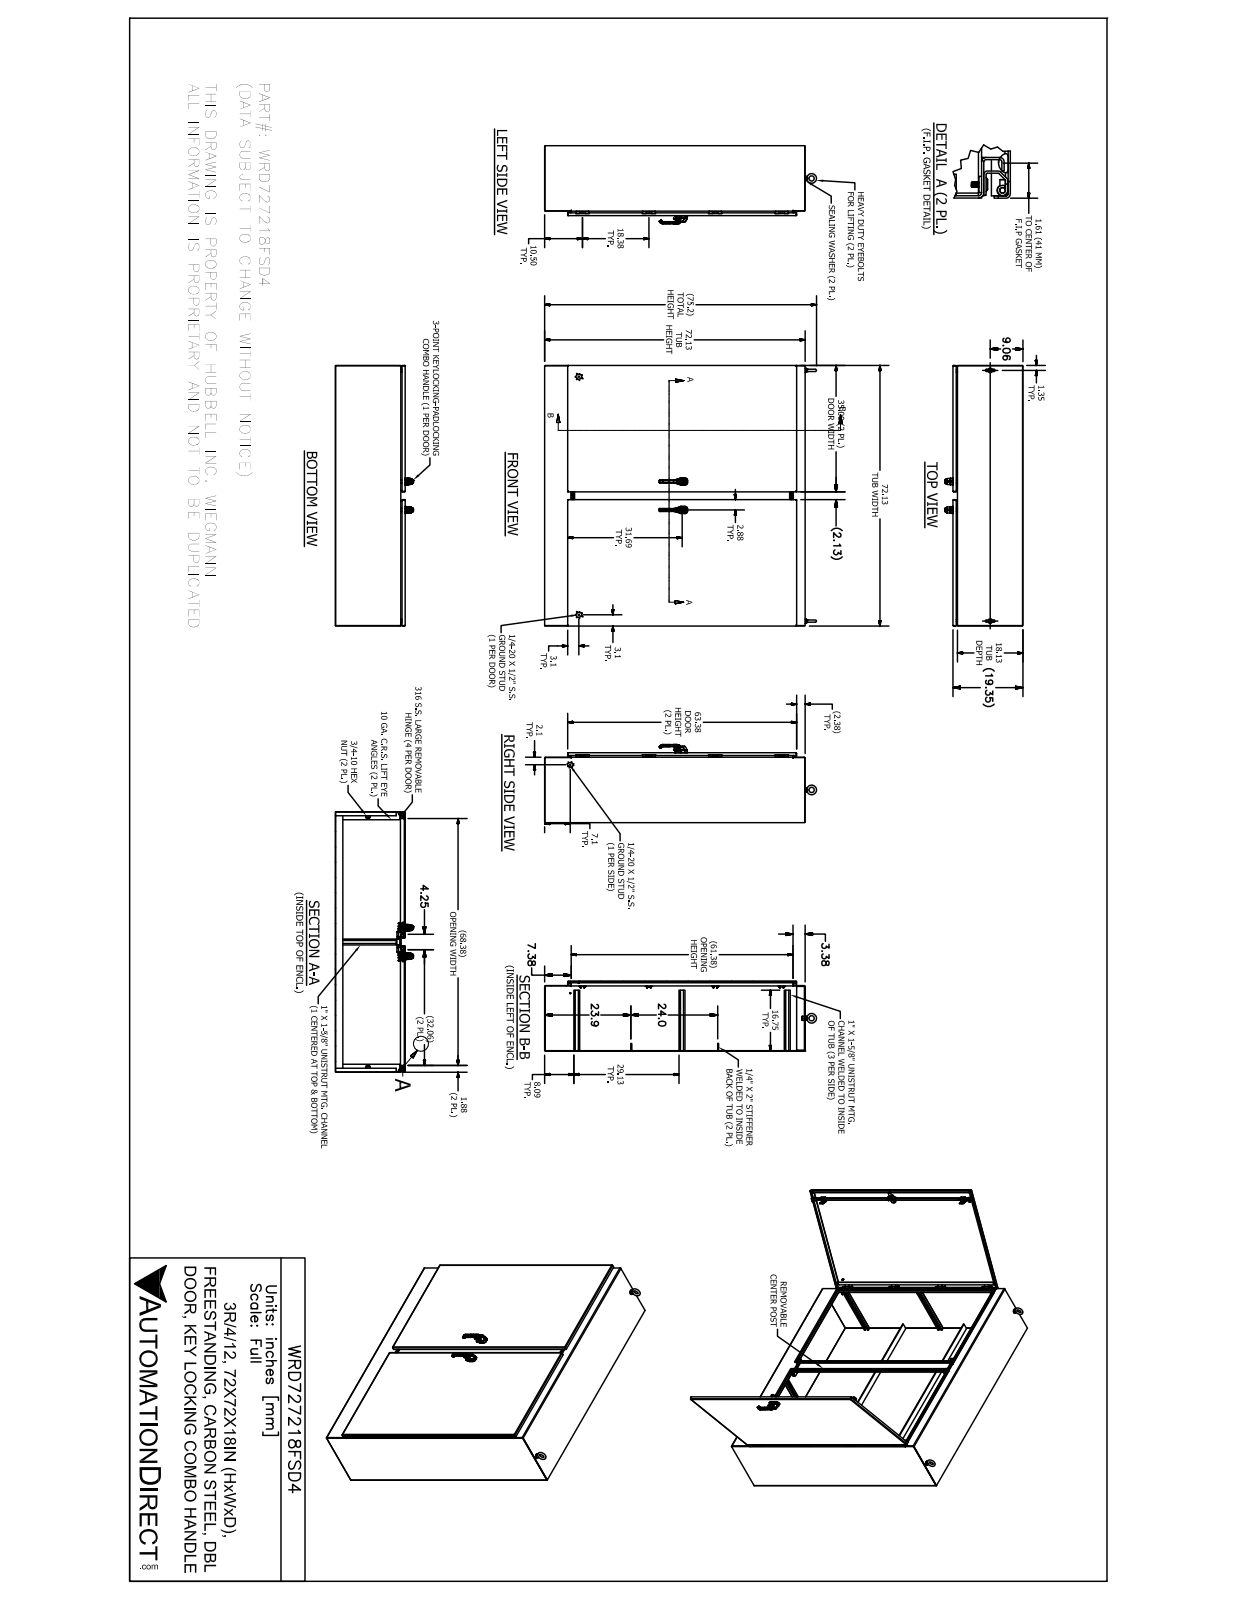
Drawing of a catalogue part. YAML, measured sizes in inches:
part_name: "WRD727218FSD4"
step_written_by: "SolidWorks 2017 (AUTOMOTIVE_DESIGN)"
units: inches
bodies: {solids: 155, faces: 3276, planar: 1520, cylindrical: 1096, other: 660}
overall_size: [75.248, 72.133, 21.527]
volume: 2098
surface_area: 38071
round_holes:
  - {diameter: 0.266, count: 20}
  - {diameter: 0.23, count: 16}
  - {diameter: 0.281, count: 16}
  - {diameter: 0.65, count: 16}
  - {diameter: 0.2, count: 8}
  - {diameter: 0.277, count: 8}
  - {diameter: 0.281, count: 6}
  - {diameter: 0.156, count: 4}
  - {diameter: 0.252, count: 4}
  - {diameter: 0.4, count: 4}
  - {diameter: 0.45, count: 4}
  - {diameter: 0.241, count: 3}
round_bosses_or_shafts:
  - {diameter: 0.625, count: 15}
  - {diameter: 0.25, count: 13}
  - {diameter: 0.533, count: 4}
  - {diameter: 0.438, count: 4}
  - {diameter: 0.375, count: 4}
  - {diameter: 0.313, count: 4}
  - {diameter: 0.213, count: 4}
  - {diameter: 1, count: 3}
partial_cylinders:
  - {radius: 0.062, count: 43}
  - {radius: 0.05, count: 32}
  - {radius: 0.125, count: 32}
  - {radius: 0.063, count: 17}
  - {radius: 0.01, count: 16}
  - {radius: 0.019, count: 16}
  - {radius: 0.025, count: 16}
  - {radius: 0.053, count: 16}
face_to_face_distances: [0.104, 19.245, 72.021, 19.141, 19.349, 71.917, 72.125, 18.021, 1.224, 17.917]
hole_center_spacings: [1, 36.75, 48.067, 55.125, 1.102, 1.195, 18.375, 28.212]
